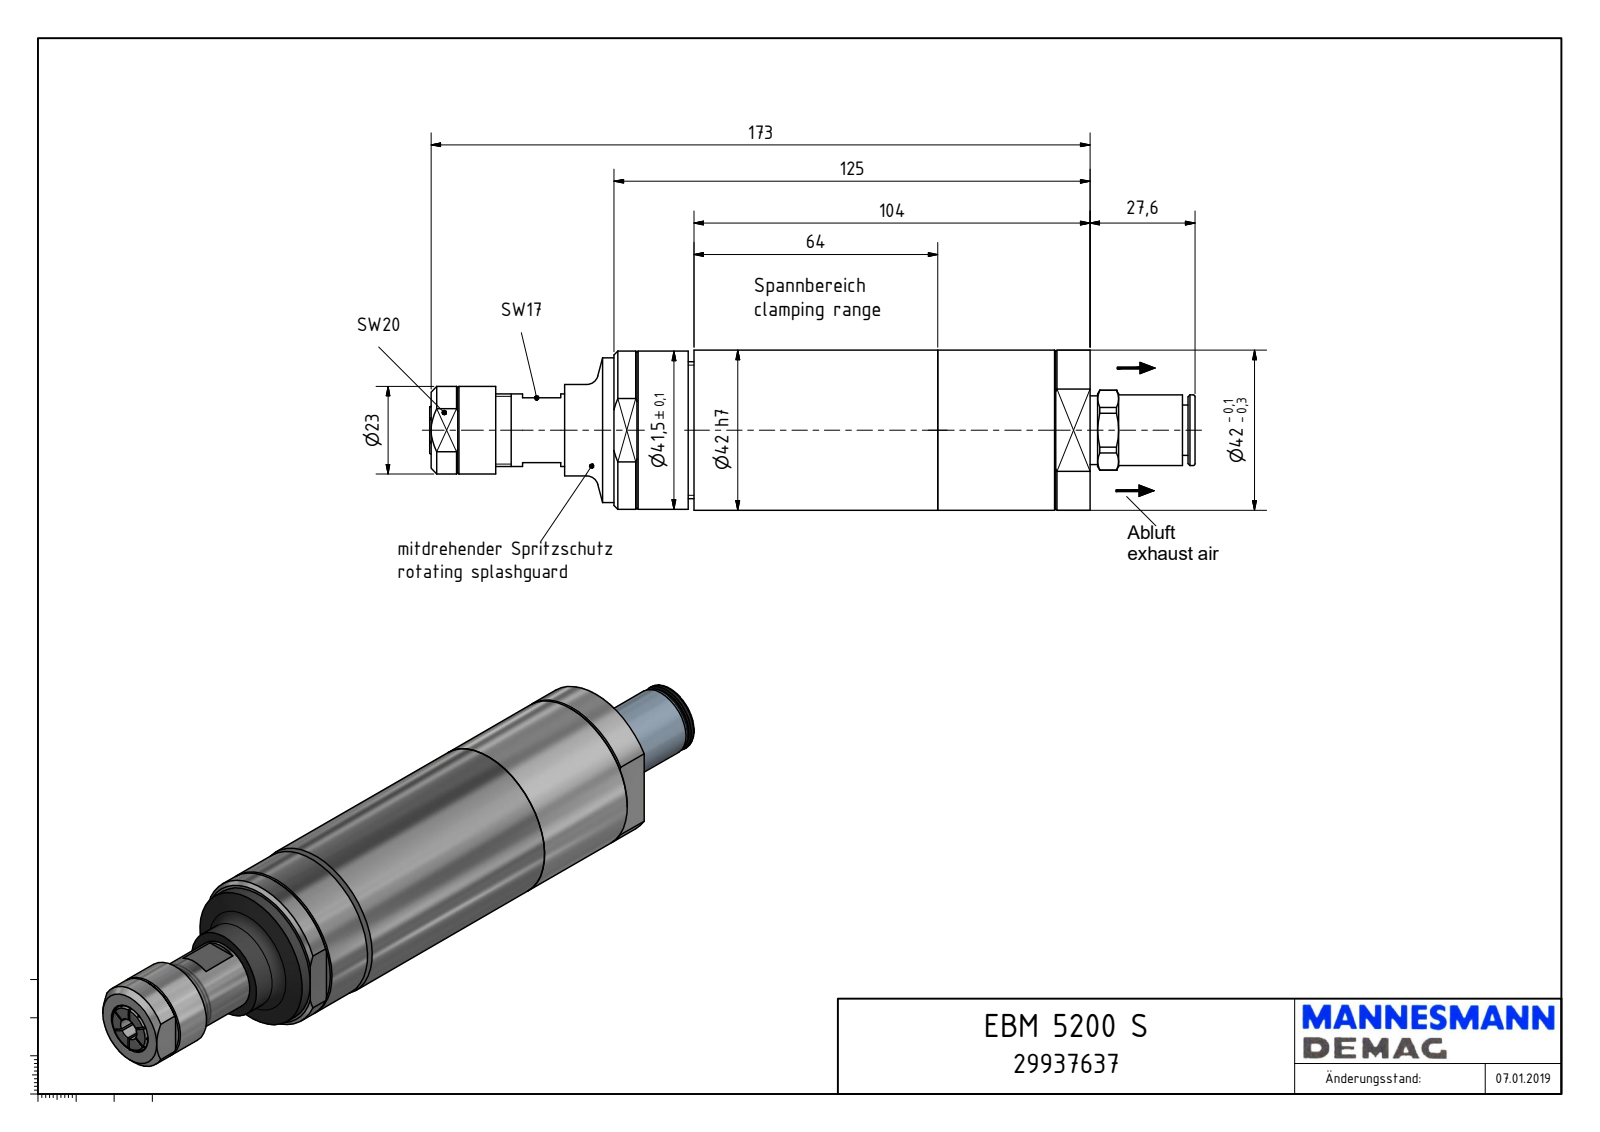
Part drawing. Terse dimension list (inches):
name: EBM 5200 S_29937637
written by: Autodesk Inventor 2018 (AUTOMOTIVE_DESIGN)
unit: in
bodies: 1 solid, 218 faces (99 planar, 55 cylindrical, 64 other)
size: 7.912 × 1.654 × 1.654
volume: 11.86 in³; area: 47.38 in²
holes: 1× ⌀0.236, 1× ⌀0.472, 1× ⌀0.52, 1× ⌀0.706, 1× ⌀0.748, 1× ⌀1.417
bosses: 1× ⌀1.654, 1× ⌀1.634, 1× ⌀1.496, 1× ⌀1.415, 1× ⌀0.945, 1× ⌀0.906, 1× ⌀0.728, 1× ⌀0.709
rounds: 6× R0.712, 6× R1.328, 1× R0.413
face distances: 0.02, 4.094, 0.059, 4.154, 0.354, 0.669, 1.417, 0.039, 1.457, 0.315
